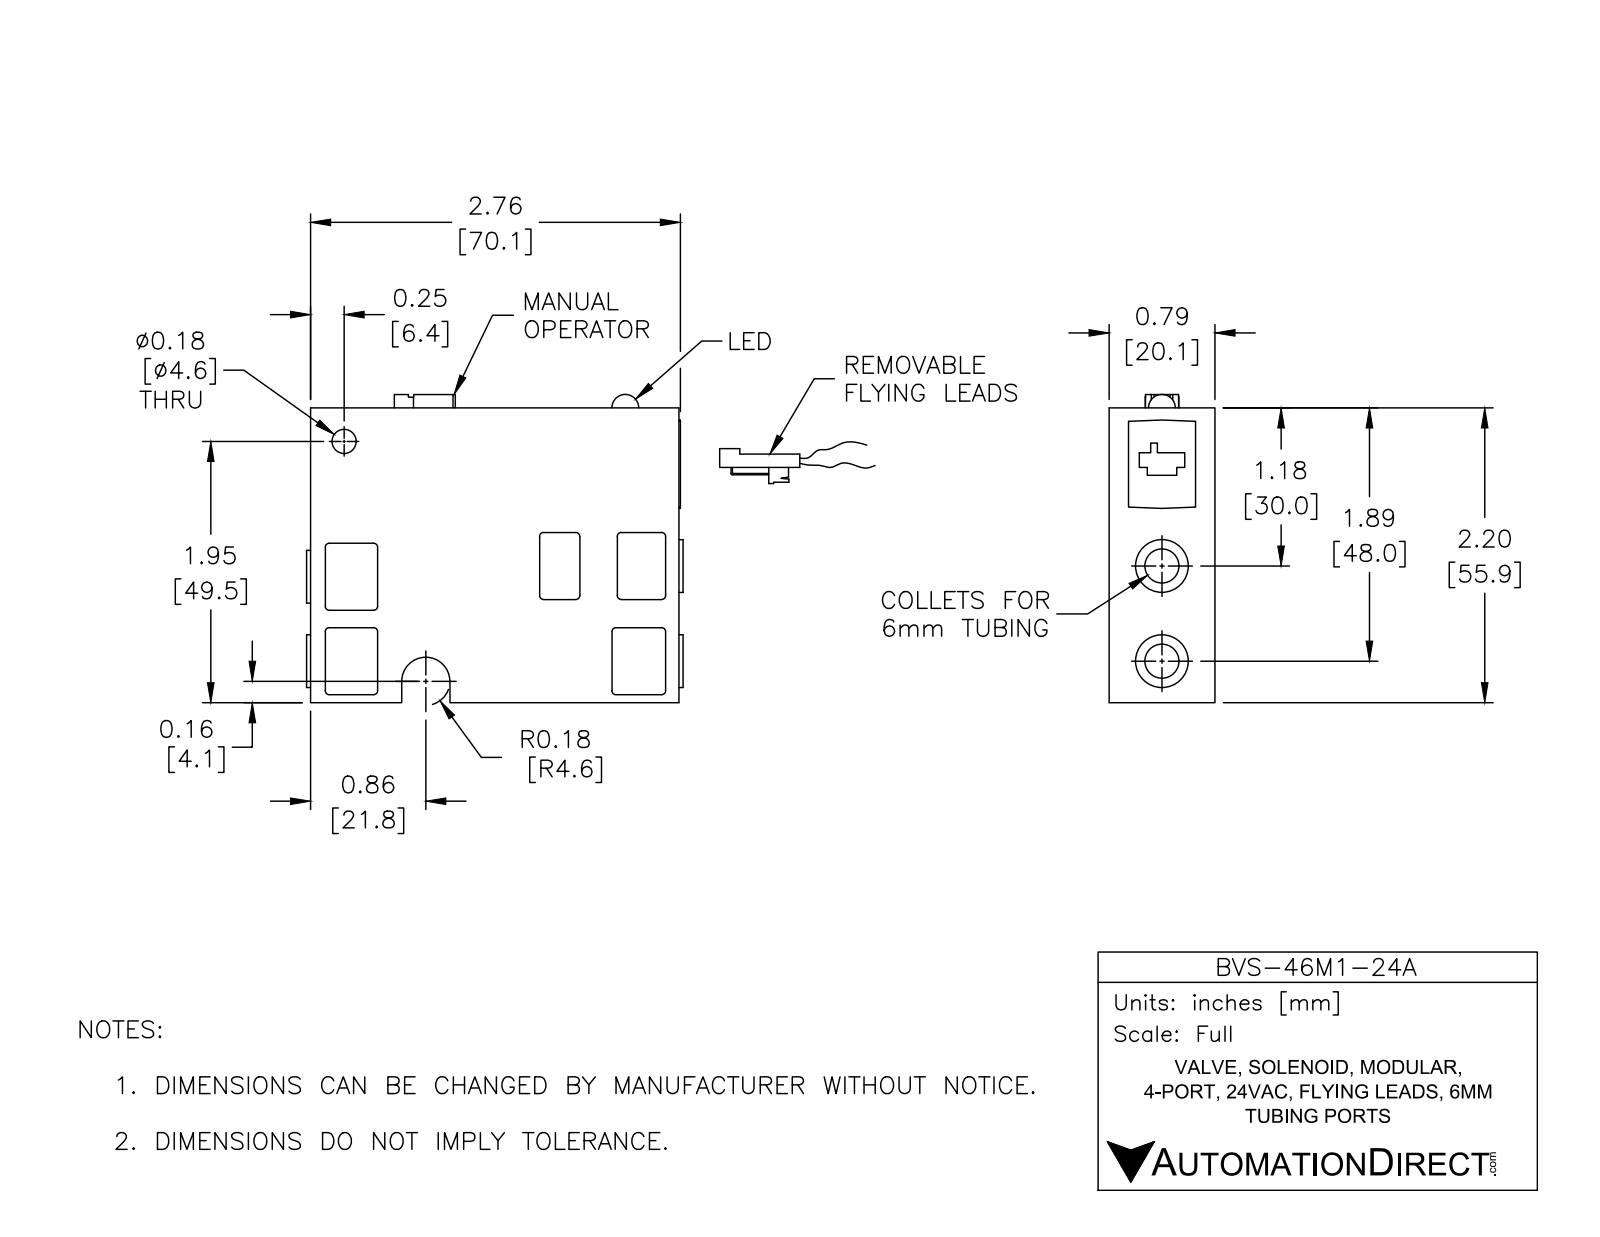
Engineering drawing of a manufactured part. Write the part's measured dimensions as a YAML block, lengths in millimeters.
part_name: "BVS-46M1-24A"
step_written_by: "SolidWorks 2016 (AUTOMOTIVE_DESIGN)"
units: millimeters
bodies: {solids: 1, faces: 173, planar: 85, cylindrical: 78, other: 10}
overall_size: [76.4, 58.4, 20.1]
volume: 71730
surface_area: 16150
round_holes:
  - {diameter: 6.4, count: 3}
  - {diameter: 2.5, count: 1}
  - {diameter: 4.6, count: 1}
round_bosses_or_shafts:
  - {diameter: 1.5, count: 6}
  - {diameter: 10, count: 3}
partial_cylinders:
  - {radius: 0.8, count: 20}
  - {radius: 0.5, count: 2}
  - {radius: 3.2, count: 1}
  - {radius: 4.6, count: 1}
face_to_face_distances: [20.1, 2.5, 55.9, 17.5, 69.9, 15, 12.7, 2.8, 67.3, 70.1]
hole_center_spacings: [2, 14, 16, 16, 18, 32]
